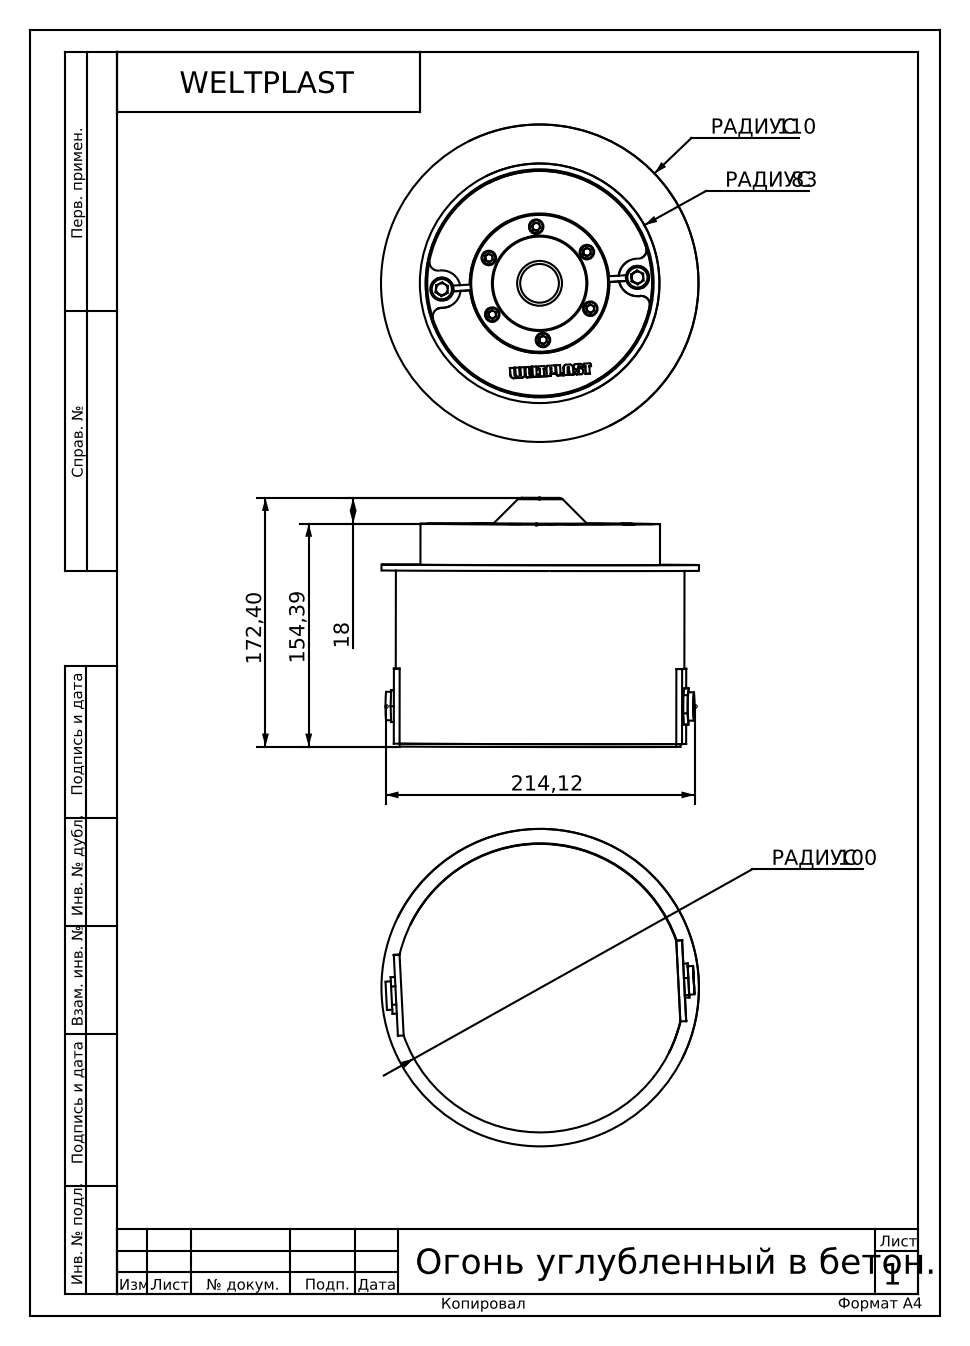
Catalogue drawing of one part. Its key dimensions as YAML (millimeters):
part_name: "socket head cap screw_am_B18.3.1M - 6 x 1.0 x 16 Hex SHCS -- 16NHX; Корпус; Сборка_стакана; Огонь углубленный в бето (+8 more)"
step_written_by: "SolidWorks 2018 (AUTOMOTIVE_DESIGN)"
units: millimeters
bodies: {solids: 23, faces: 1534, planar: 485, cylindrical: 503, other: 546}
overall_size: [220, 220, 172.35]
volume: 1168000
surface_area: 483114
round_holes:
  - {diameter: 6, count: 12}
  - {diameter: 10, count: 6}
  - {diameter: 12.6, count: 4}
  - {diameter: 2, count: 2}
  - {diameter: 2.5, count: 2}
  - {diameter: 3, count: 2}
  - {diameter: 9, count: 2}
  - {diameter: 11, count: 2}
  - {diameter: 20, count: 2}
  - {diameter: 21, count: 2}
  - {diameter: 8.15, count: 1}
  - {diameter: 96.8, count: 1}
round_bosses_or_shafts:
  - {diameter: 21.5, count: 4}
  - {diameter: 19.7, count: 4}
  - {diameter: 16, count: 2}
  - {diameter: 10, count: 2}
  - {diameter: 220, count: 1}
  - {diameter: 200, count: 1}
  - {diameter: 166, count: 1}
  - {diameter: 155.8, count: 1}
partial_cylinders:
  - {radius: 3, count: 20}
  - {radius: 0.5, count: 14}
  - {radius: 0.7, count: 4}
  - {radius: 6, count: 4}
  - {radius: 1.5, count: 2}
  - {radius: 13, count: 2}
  - {radius: 11.82, count: 1}
face_to_face_distances: [4, 124, 2, 126, 122, 120, 28.35, 32.35, 154.35, 152.35]
hole_center_spacings: [39.32, 48, 62.05, 24.11, 84.37, 68.1, 83.14, 24.1]
